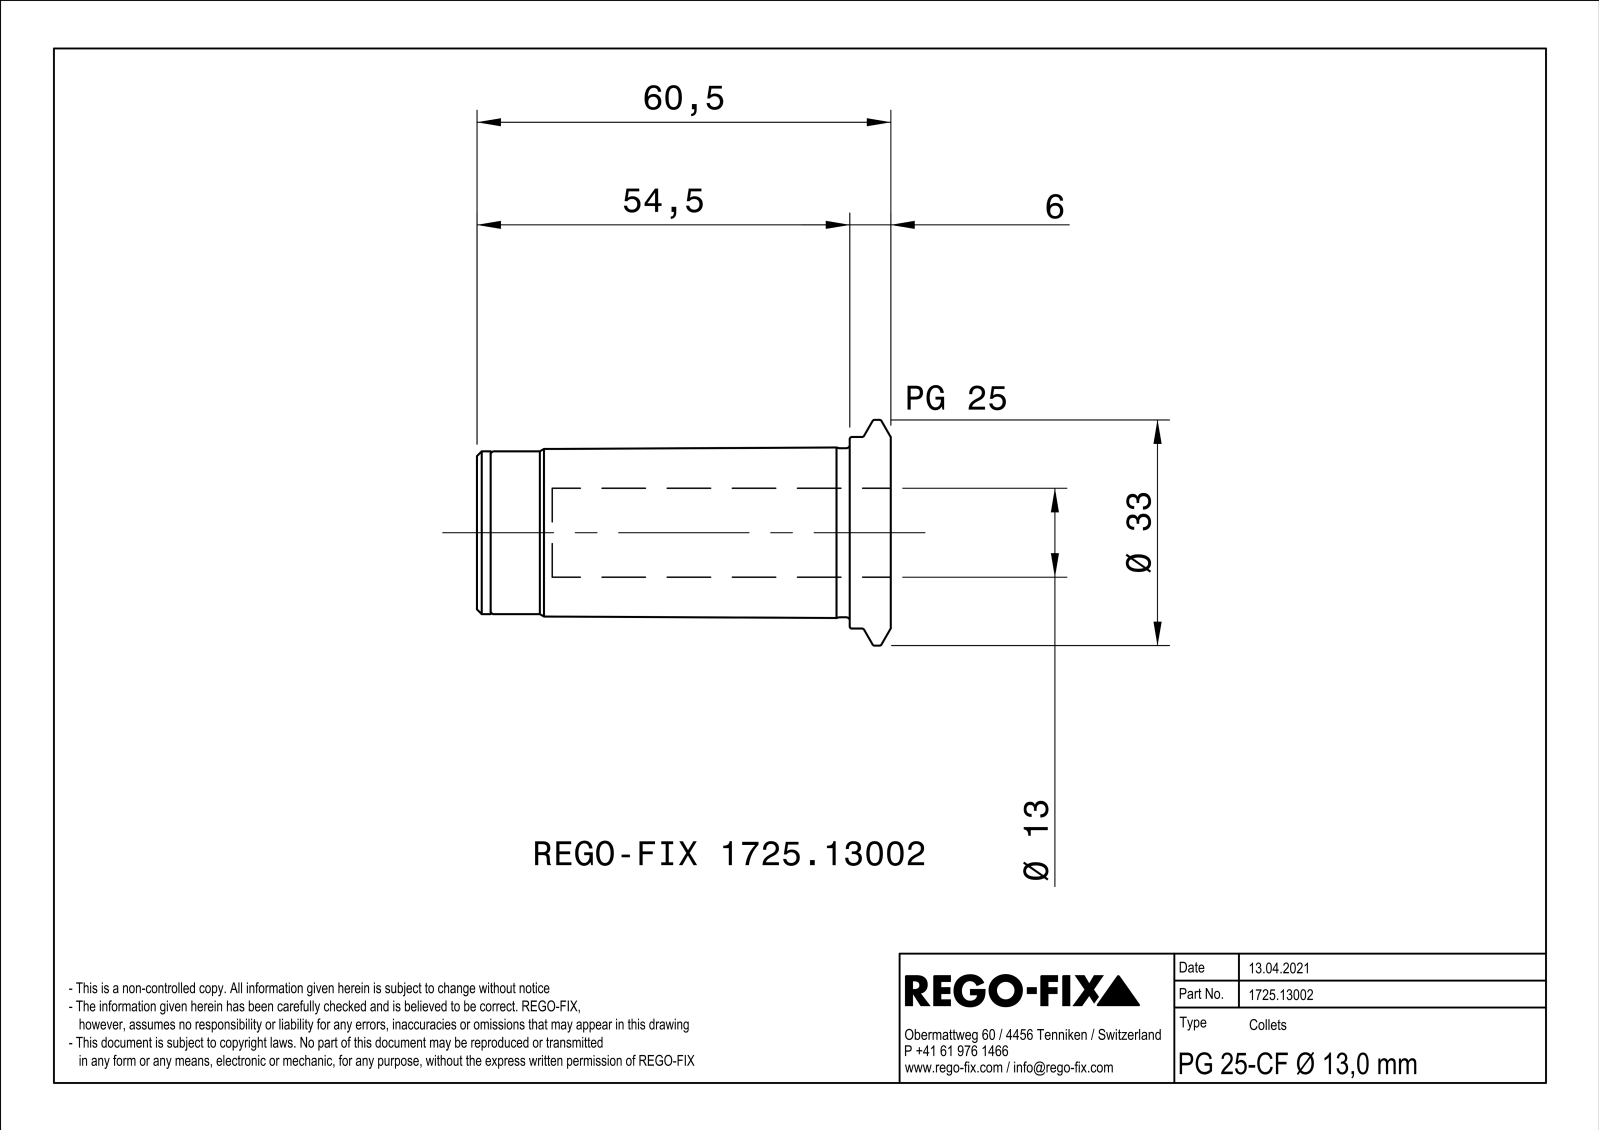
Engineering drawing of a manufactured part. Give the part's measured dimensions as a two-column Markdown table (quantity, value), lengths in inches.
| quantity | value |
| --- | --- |
| part name | NOCUT |
| STEP written by | SIEMENS PLM Software Solid Edge ST10 (AUTOMOTIVE_DESIGN) |
| units | inches |
| bodies | 1 solid, 89 faces (23 planar, 27 cylindrical, 39 other) |
| overall size | 2.382 × 1.299 × 1.299 |
| volume | 1.298 in³ |
| surface area | 17.35 in² |
| round holes (diameter × count) | 0.098 × 3, 0.205 × 1, 0.272 × 1, 0.323 × 1, 0.512 × 1, 0.824 × 1, 0.874 × 1 |
| round bosses / shafts (diameter × count) | 1.299 × 1, 1.102 × 1, 0.972 × 1, 0.937 × 1, 0.803 × 1, 0.472 × 1 |
| partial cylindrical surfaces (radius × count) | 0.03 × 3 |
| main face-to-face distances | 0.039, 2.382, 2.071, 0.311, 2.303, 0.232, 0.079, 1.969, 0.102, 0.335 |
| hole center spacings | 0.305, 0.529, 0.528 |
